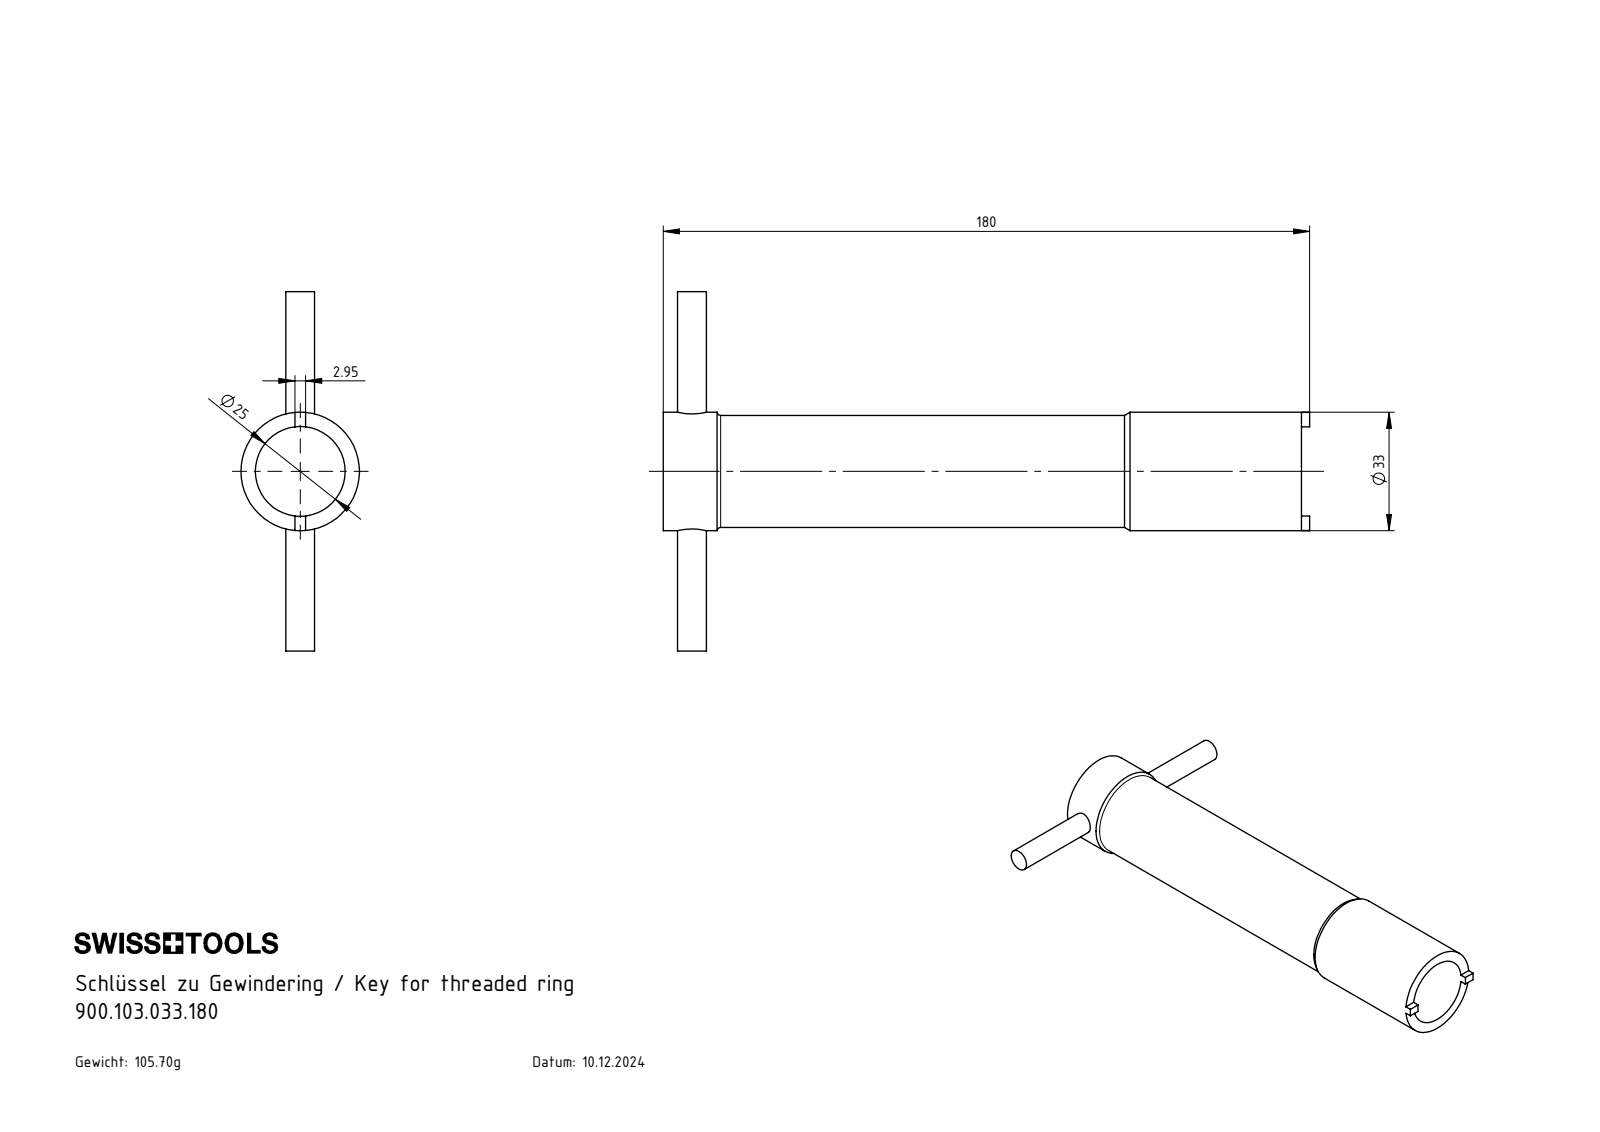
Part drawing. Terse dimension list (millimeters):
name: 900.103.033.180
written by: SolidWorks 2022 (CONFIG_CONTROL_DESIGN)
unit: mm
bodies: 1 solid, 29 faces (11 planar, 12 cylindrical, 6 other)
size: 180 × 100 × 33
volume: 105 705 mm³; area: 27 505 mm²
holes: 1× ⌀25
bosses: 1× ⌀33, 1× ⌀31.2, 1× ⌀8
face distances: 177.7, 100, 2.3, 180, 2.96
